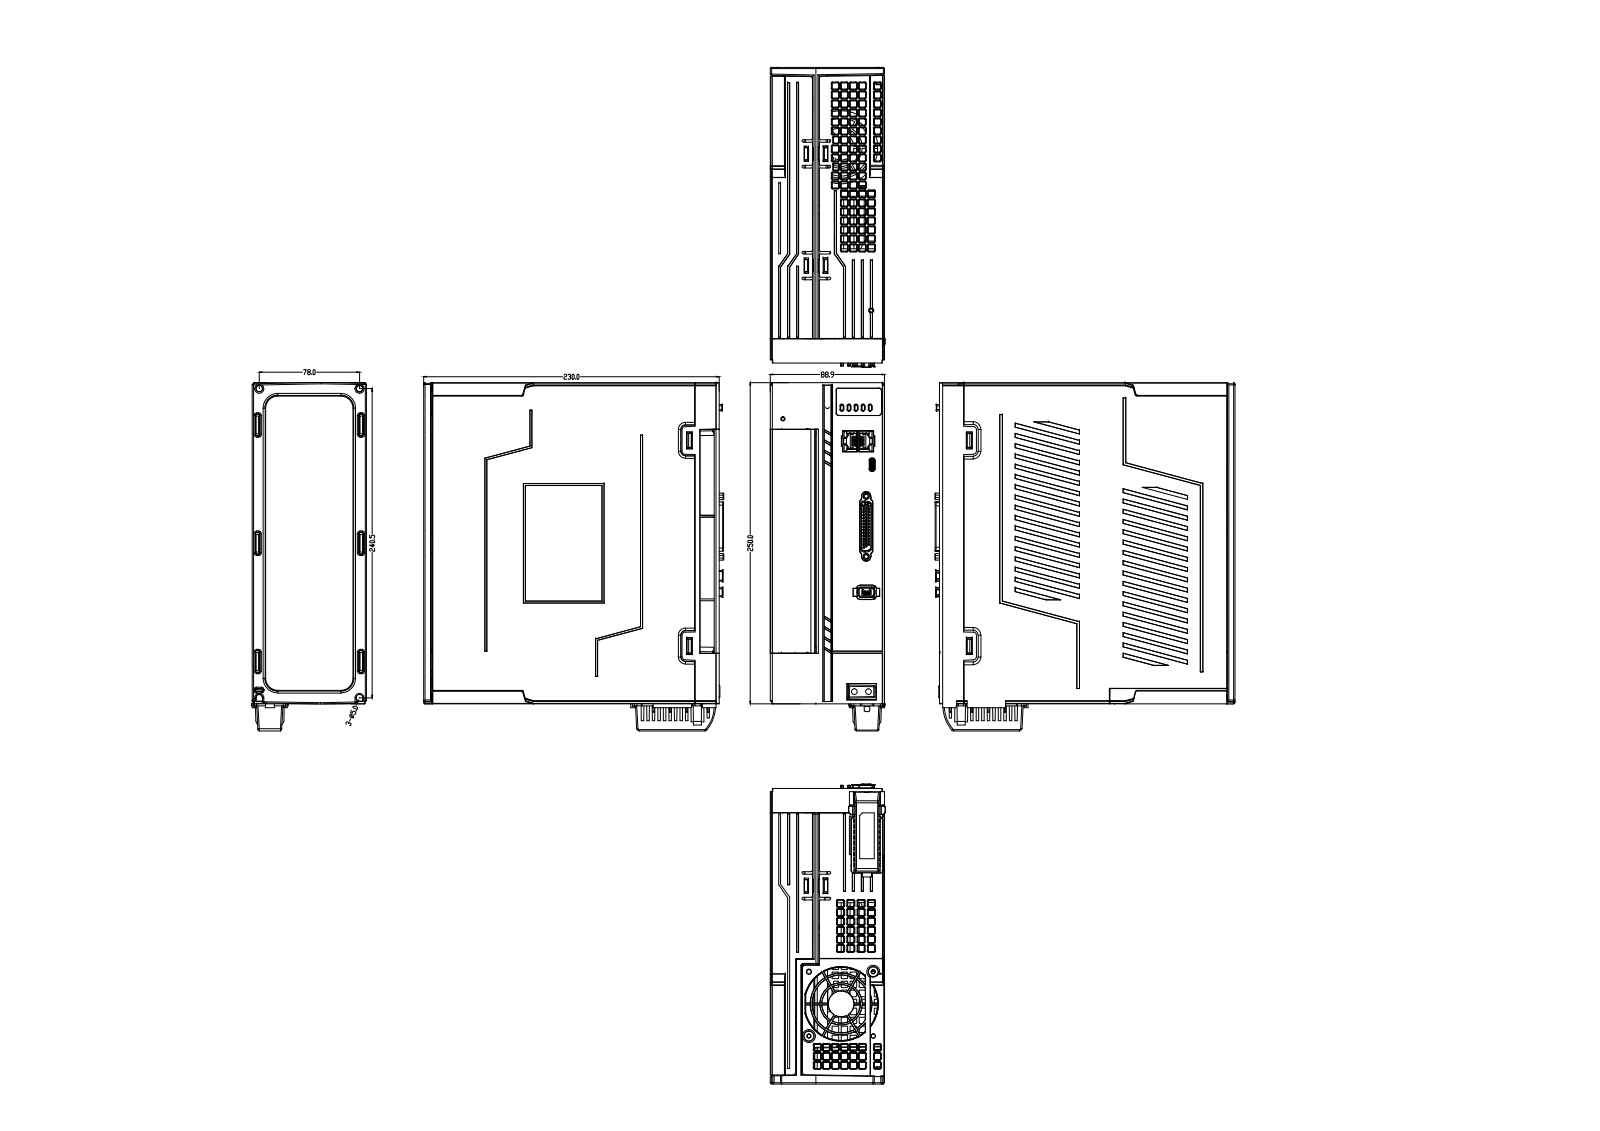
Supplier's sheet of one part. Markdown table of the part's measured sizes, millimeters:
| quantity | value |
| --- | --- |
| part name | MANIFOLD_SOLID_BREP_21900; FF_L7P_7500T_11; FF_L7P_7500T_11_ASM_ASM_ASM_ASM; MANIFOLD_SOLID_BREP_835_1 (+8 more) |
| STEP written by | PRO/ENGINEER BY PARAMETRIC TECHNOLOGY CORPORATION, 2010280 (CONFIG_CONTROL_DESIGN) |
| units | millimeters |
| bodies | 21 solids, 10190 faces (6130 planar, 2014 cylindrical, 2046 other) |
| overall size | 271.03 × 233.48 × 89.49 |
| volume | 1 376 000 mm³ |
| surface area | 880 383 mm² |
| round holes (diameter × count) | 0.73 × 44, 2.2 × 19, 3.5 × 18, 2.5 × 13, 3.2 × 4, 0.57 × 3, 2.8 × 2, 2.84 × 2, 4.5 × 2, 5.5 × 2, 2.48 × 1 |
| round bosses / shafts (diameter × count) | 6.8 × 13, 2.5 × 12, 4.2 × 5, 10 × 4, 16.2 × 2, 0.5 × 2 |
| partial cylindrical surfaces (radius × count) | 0.5 × 349, 1 × 240, 0.3 × 51, 0.15 × 42, 0.2 × 39, 2 × 39, 0.4 × 37, 1.8 × 24 |
| main face-to-face distances | 2.5, 86.4, 2, 7.5, 78.9, 88.9, 81.4, 5, 83.9, 7 |
| hole center spacings | 2.29, 4.58, 4.57, 2.21, 2.37, 3.83, 6.05, 6.87 |
